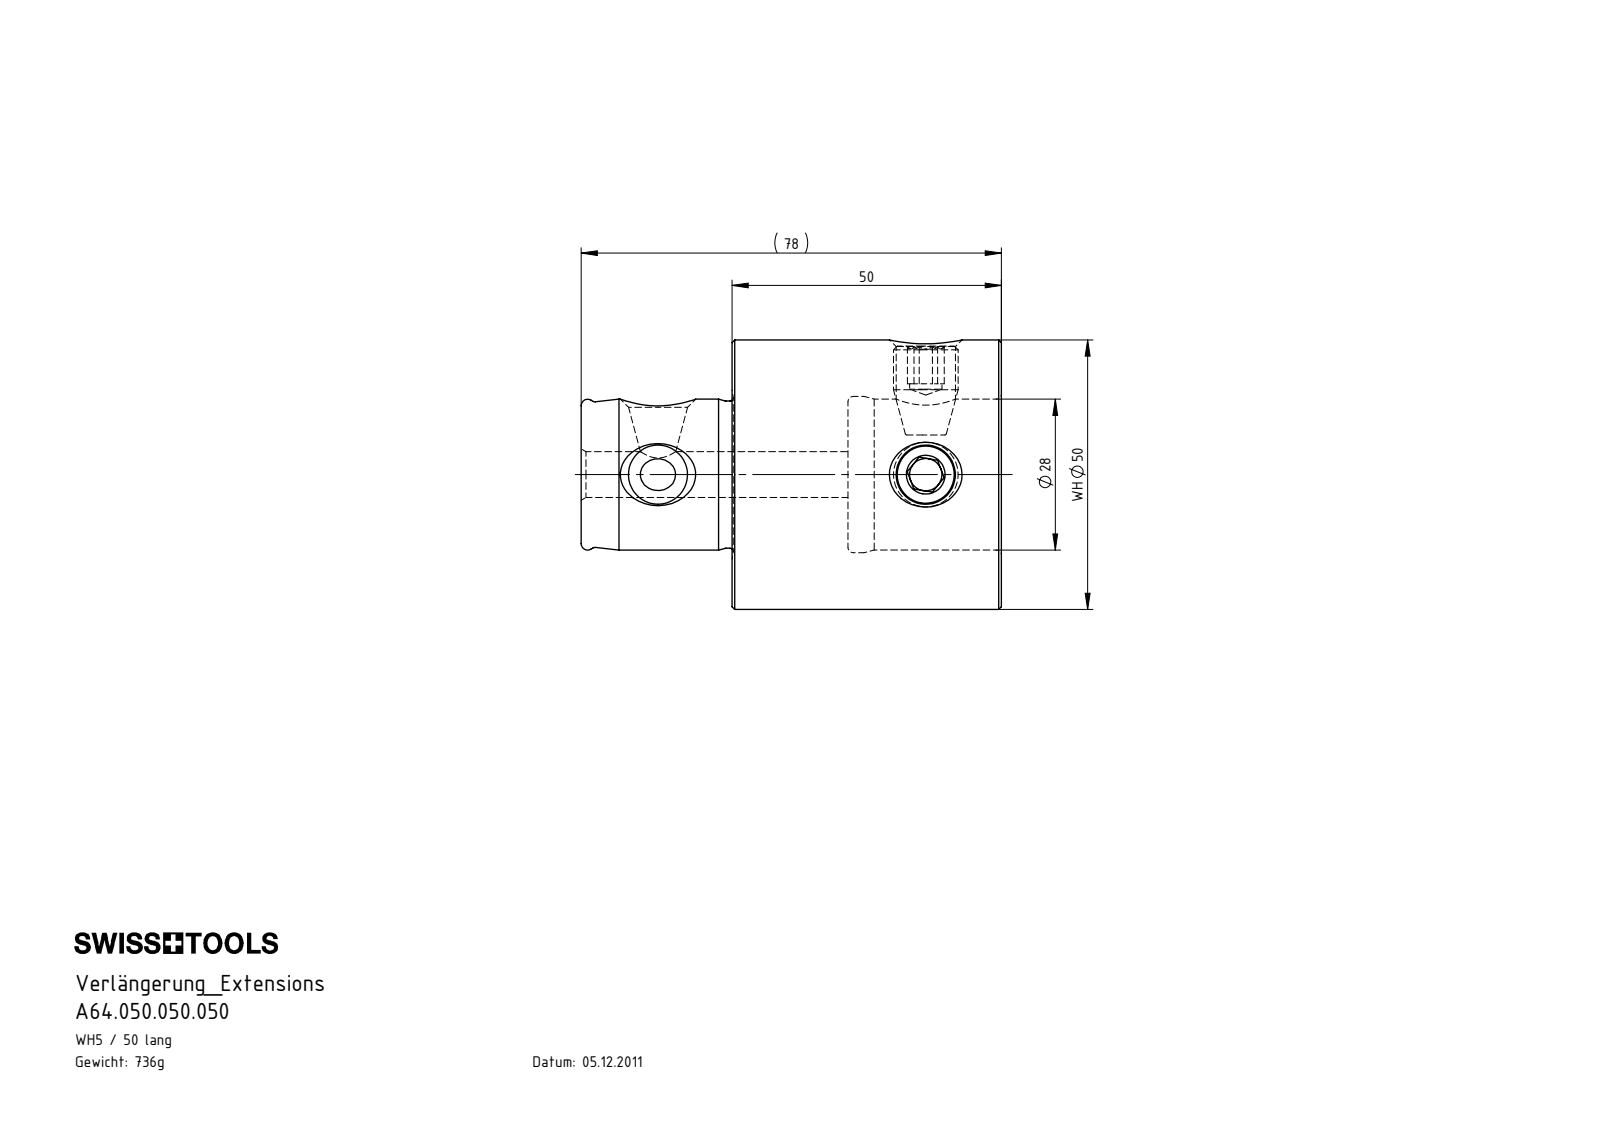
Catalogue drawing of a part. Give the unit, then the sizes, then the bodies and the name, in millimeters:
Units: millimetres
Overall size (bounding box): 78 × 50 × 50
Round holes (diameter × count): ⌀11 ×2, ⌀8.5 ×1, ⌀28 ×1, ⌀29 ×1
Round bosses / shafts (diameter × count): ⌀12 ×2, ⌀50 ×1, ⌀27.3 ×1
Main face-to-face distances: 50, 21.5, 28.5, 28, 49.5, 78, 6, 16.5, 9.5, 7
Volume: 93 838 mm³ · Surface area: 20 198 mm²
Bodies: 3 solids, 94 faces (22 planar, 20 cylindrical, 52 other)
Part name (STEP PRODUCT): WH5-WH5.001.050; WH5-ER1.001.017; WH5-WH5.001.050_A
STEP written by: SolidWorks 2015 (AUTOMOTIVE_DESIGN)
